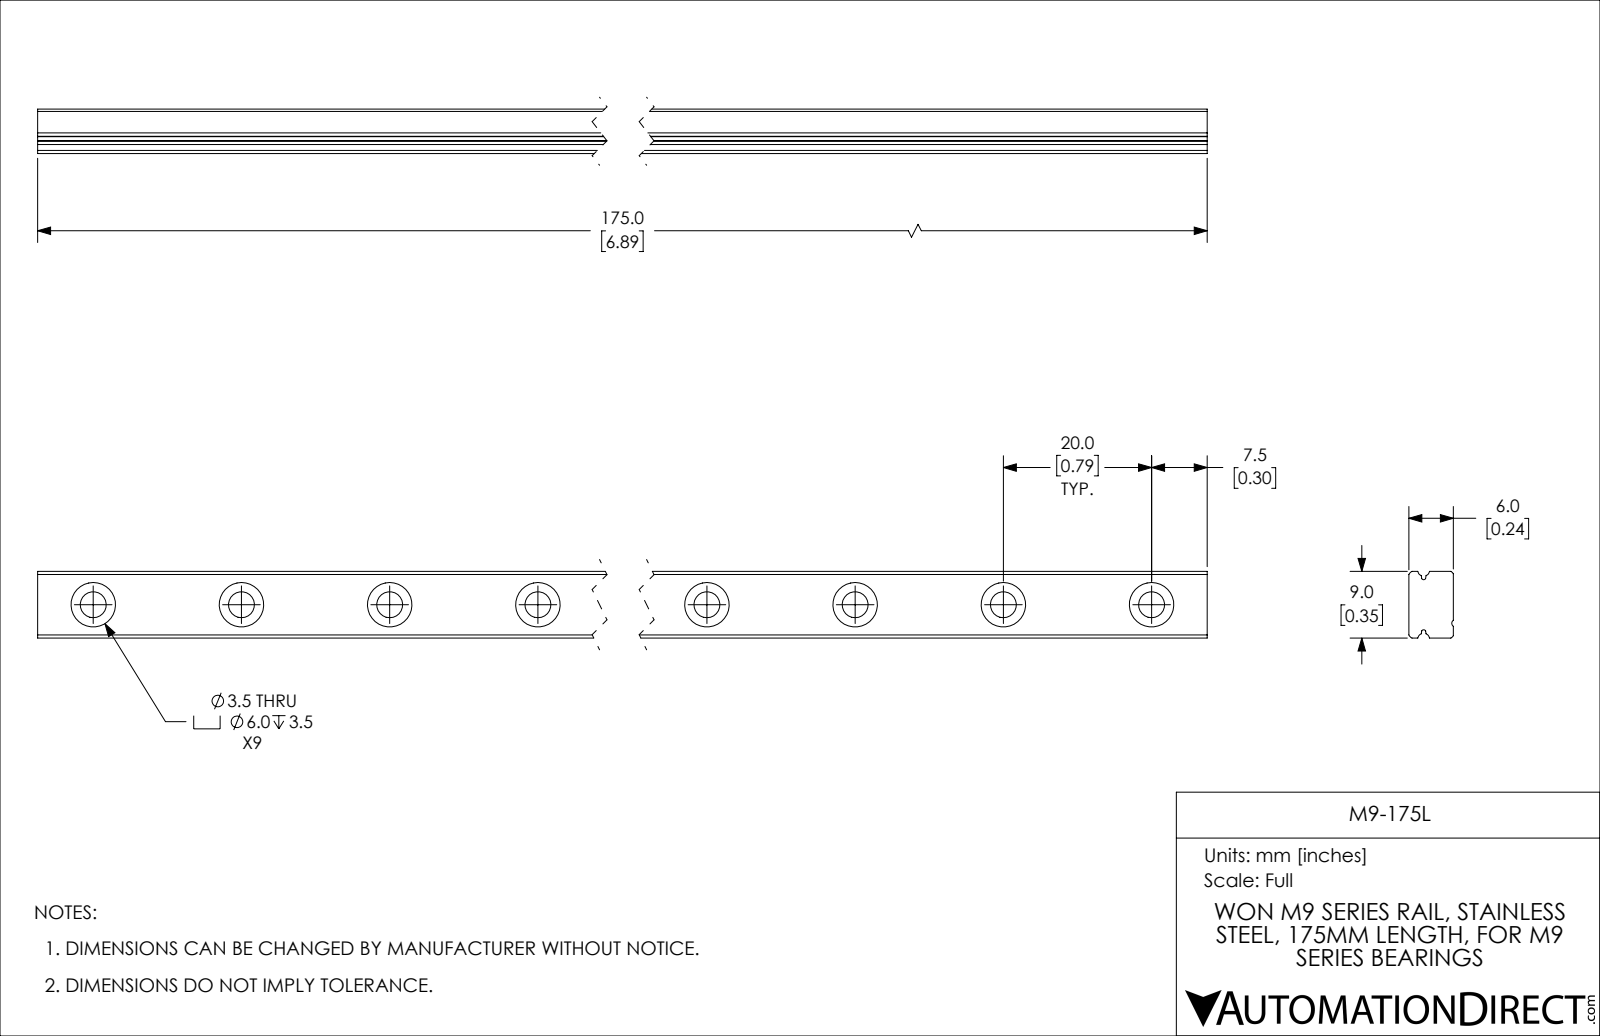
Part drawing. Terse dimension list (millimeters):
name: M9-175L
written by: SolidWorks 2019 (CONFIG_CONTROL_DESIGN)
unit: mm
bodies: 1 solid, 70 faces (22 planar, 48 cylindrical, 0 other)
size: 175 × 9 × 6
volume: 7 924 mm³; area: 6 386 mm²
holes: 9× ⌀3.5, 9× ⌀6
rounds: 2× R0.32, 2× R0.8, 2× R0.95, 2× R1, 1× R0.5
face distances: 6, 9, 2.5, 3.5, 0.41, 175
hole spacings: 20, 40, 60, 80, 100, 120, 140, 160
